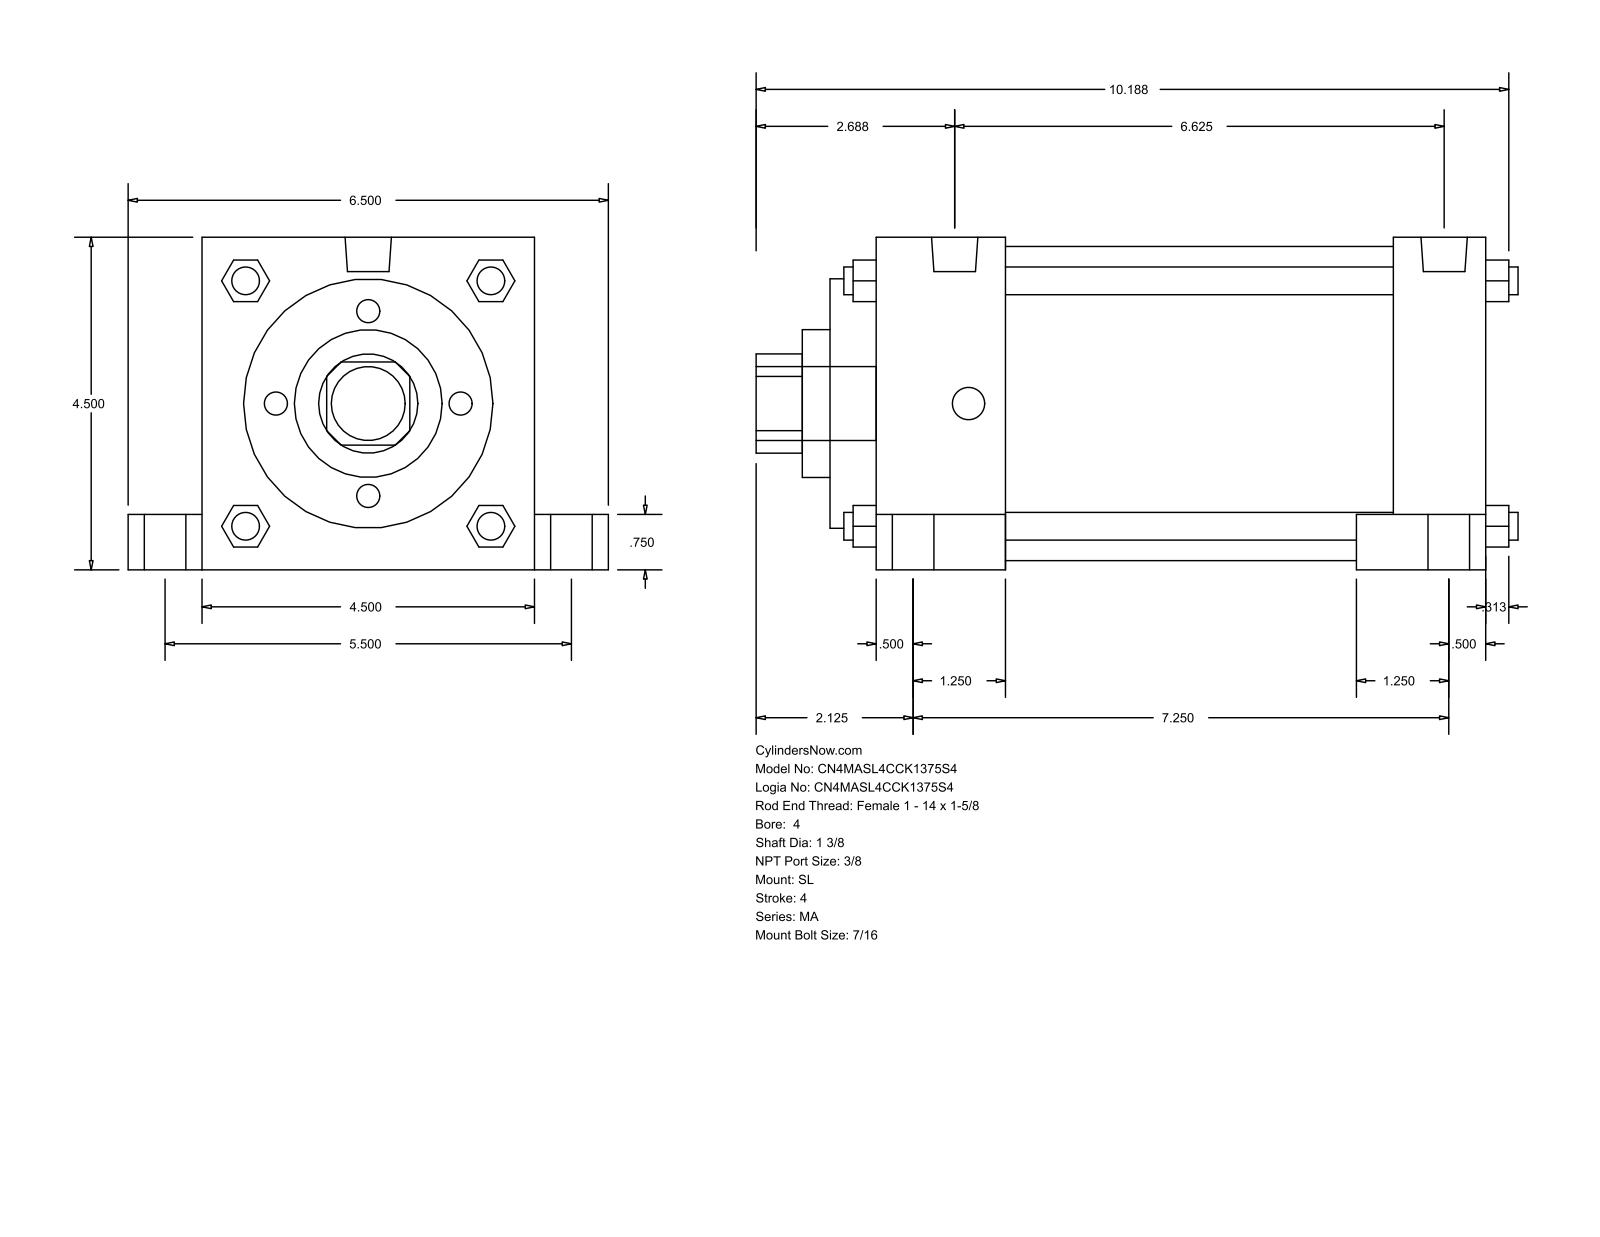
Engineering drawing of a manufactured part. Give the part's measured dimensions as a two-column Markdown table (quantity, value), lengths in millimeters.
| quantity | value |
| --- | --- |
| part name | MA_SL__0400_1.375 |
| STEP written by | GSSL Pune (CONFIG_CONTROL_DESIGN) |
| units | millimeters |
| bodies | 0 solids, 150 faces (113 planar, 37 cylindrical, 0 other) |
| overall size | 261.94 × 165.1 × 114.3 |
| round holes (diameter × count) | 34.92 × 1, 50.8 × 1, 85.72 × 1, 107.95 × 1 |
| round bosses / shafts (diameter × count) | 20.64 × 4, 14.29 × 4, 11.11 × 4, 9.53 × 4, 15.93 × 2, 25.4 × 1 |
| partial cylindrical surfaces (radius × count) | 17.06 × 1 |
| main face-to-face distances | 114.3, 209.55, 165.1, 133.35, 225.42, 15.87, 60.32, 44.45, 193.67, 177.8 |
